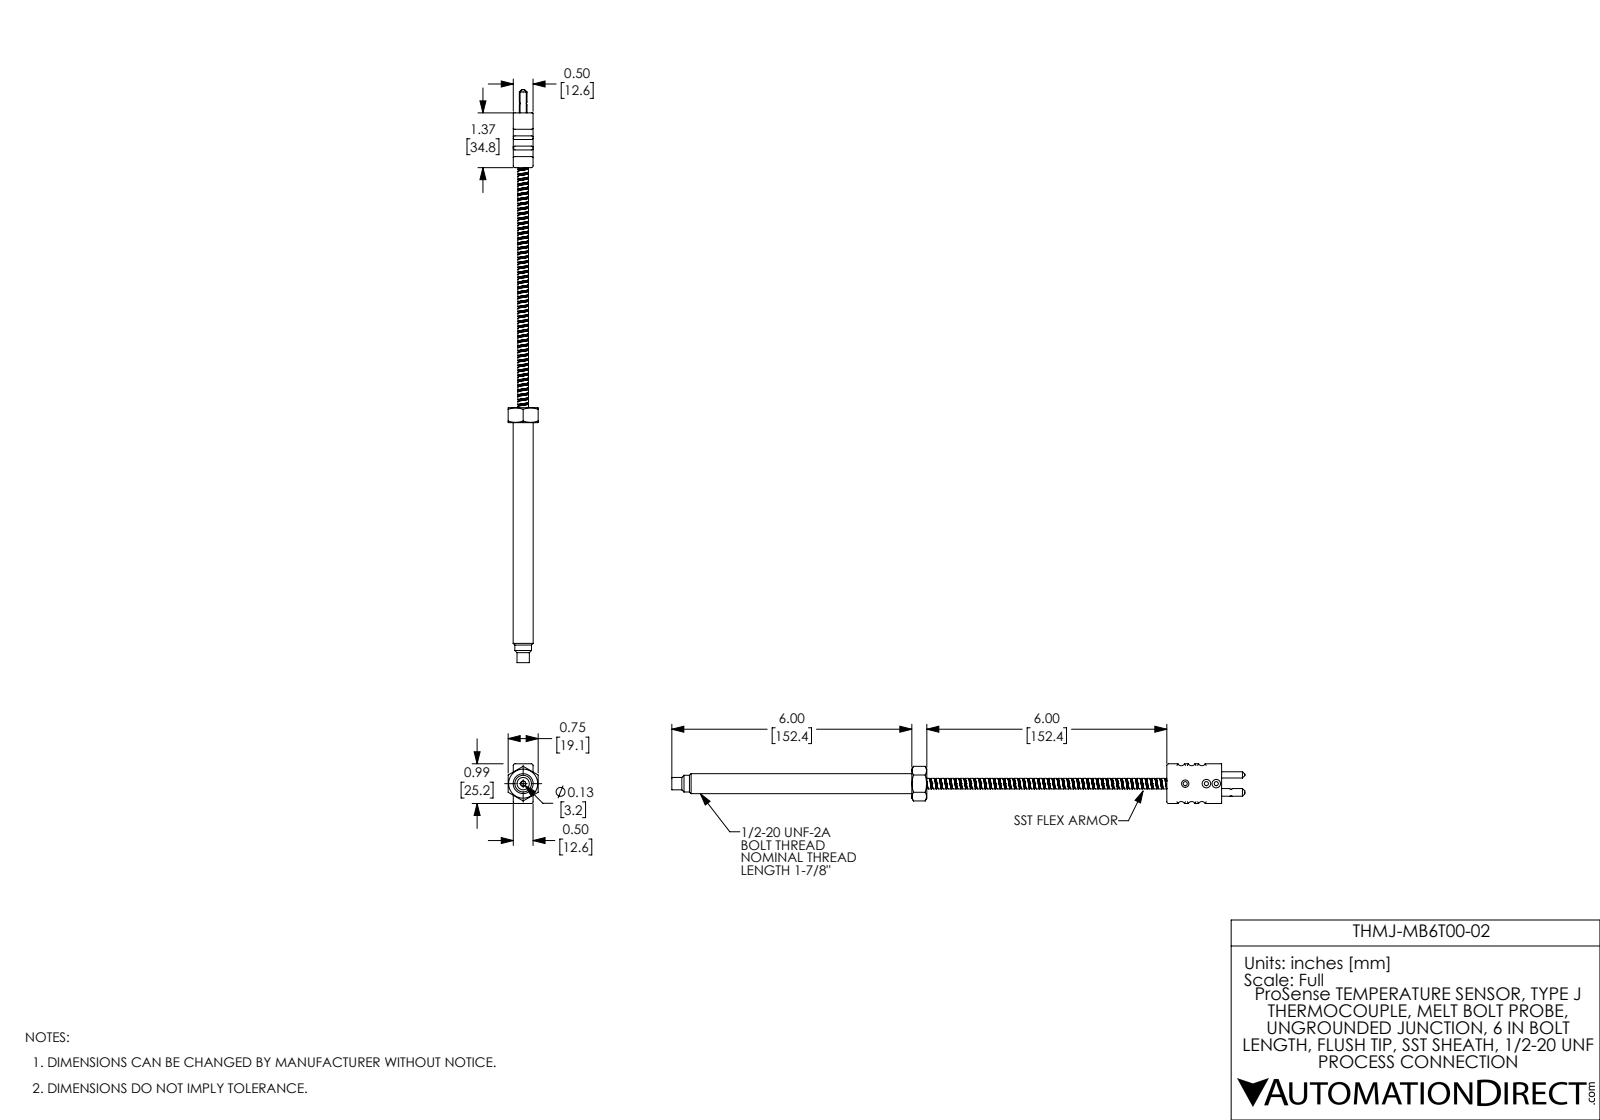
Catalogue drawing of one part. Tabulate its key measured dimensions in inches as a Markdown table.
| quantity | value |
| --- | --- |
| part name | THMJ-MB6T00-02 |
| STEP written by | SolidWorks 2017 (AUTOMOTIVE_DESIGN) |
| units | inches |
| bodies | 3 solids, 312 faces (69 planar, 172 cylindrical, 71 other) |
| overall size | 14.326 × 0.993 × 0.75 |
| volume | 2.271 in³ |
| surface area | 23.83 in² |
| round holes (diameter × count) | 0.103 × 2, 0.158 × 2, 0.135 × 1, 0.185 × 1, 0.294 × 1, 0.308 × 1 |
| round bosses / shafts (diameter × count) | 0.5 × 1, 0.417 × 1, 0.309 × 1, 0.278 × 1, 0.265 × 1, 0.191 × 1, 0.156 × 1, 0.125 × 1 |
| partial cylindrical surfaces (radius × count) | 0.045 × 8, 0.095 × 6, 0.01 × 4 |
| main face-to-face distances | 0.495, 0.75, 7.369, 6, 0.993, 0.127, 0.622, 1.369, 6.375, 7.744 |
| hole center spacings | 0.217, 0.328, 0.572, 0.247, 0.433, 0.529, 0.776 |
